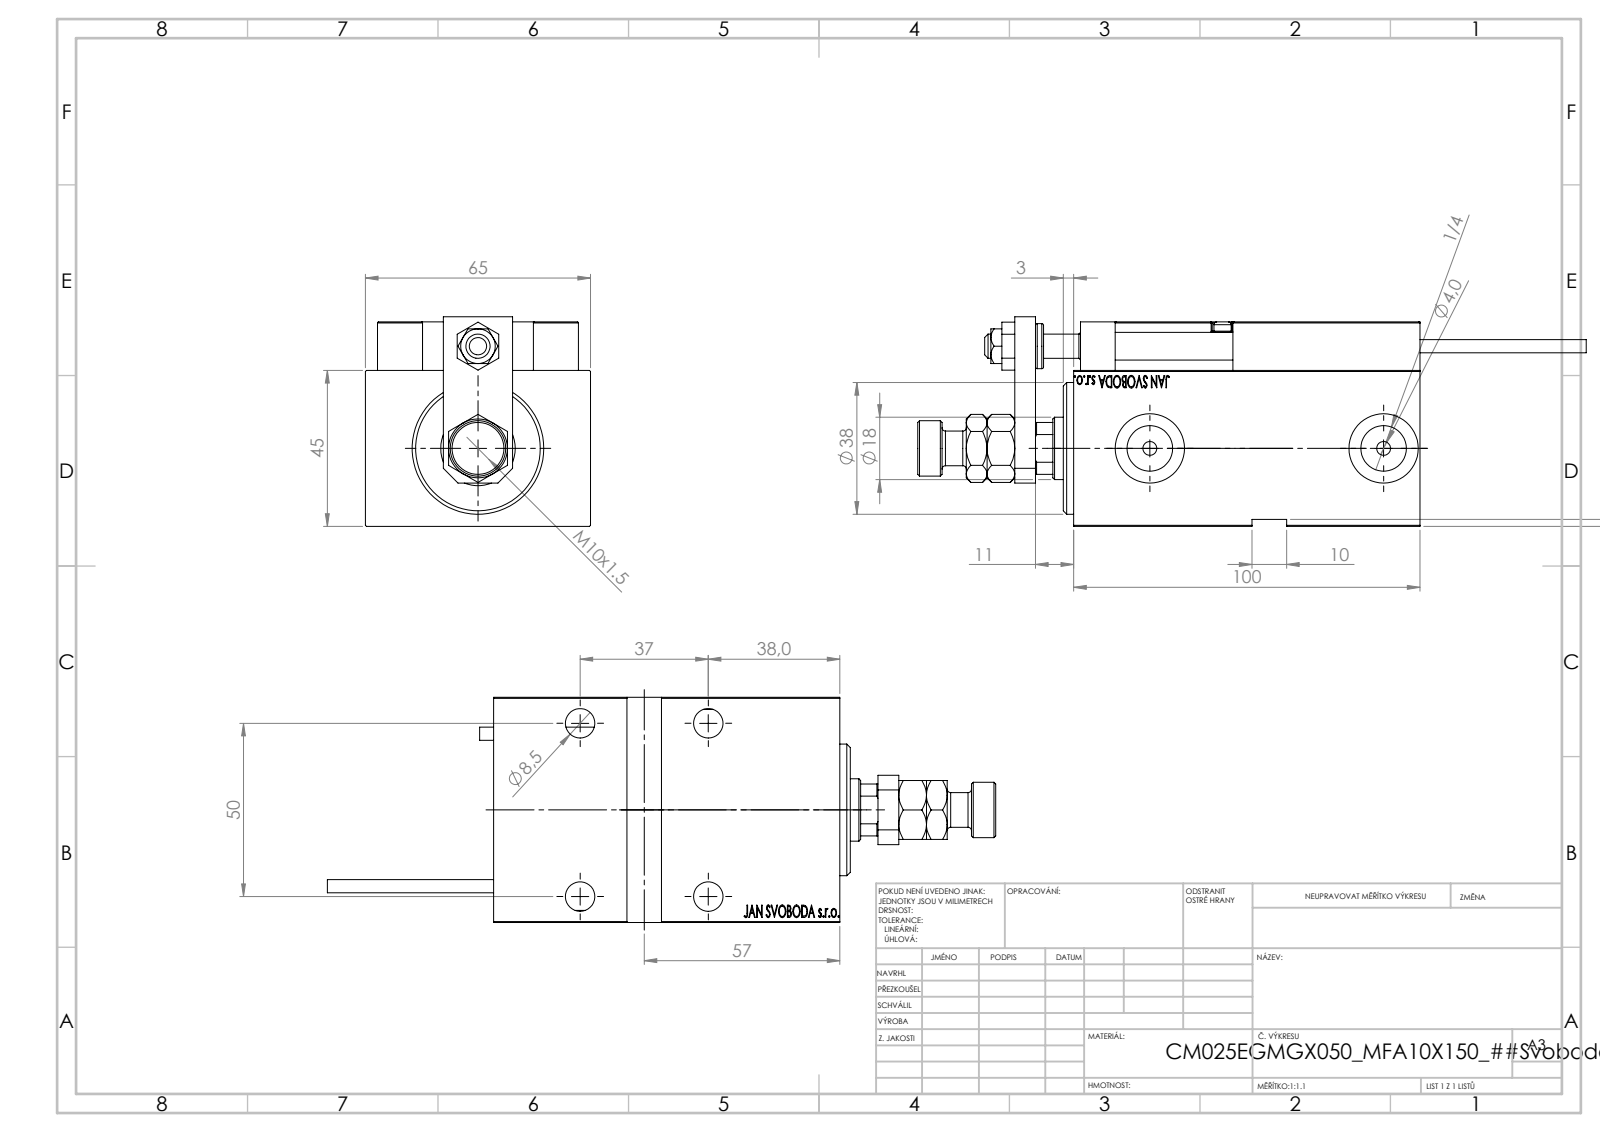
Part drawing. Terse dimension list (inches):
name: ZARAZKA; V450CM_VC_B; X_Y_MFA; TYC_L79 (+8 more)
written by: SolidWorks 2019 (CONFIG_CONTROL_DESIGN)
unit: in
bodies: 25 solids, 1345 faces (586 planar, 186 cylindrical, 573 other)
size: 7.598 × 2.559 × 2.382
volume: 19.5 in³; area: 125.2 in²
holes: 6× ⌀0.157, 5× ⌀0.315, 5× ⌀0.335, 4× ⌀0.126, 4× ⌀0.531, 2× ⌀0.197, 2× ⌀0.518, 2× ⌀0.787, 1× ⌀0.276, 1× ⌀0.571, 1× ⌀0.709, 1× ⌀0.846
bosses: 2× ⌀0.197, 2× ⌀0.15, 1× ⌀1.496, 1× ⌀1.063, 1× ⌀0.63, 1× ⌀0.512, 1× ⌀0.433, 1× ⌀0.394
rounds: 30× R0.012, 2× R0.118, 1× R0.335
face distances: 1.772, 2.559, 0.551, 2.323, 0.236, 3.937, 0.512, 0.138, 4.37, 0.394
hole spacings: 1.587, 0.448, 0.787, 0.984, 1.165, 1.169, 1.356, 1.42
